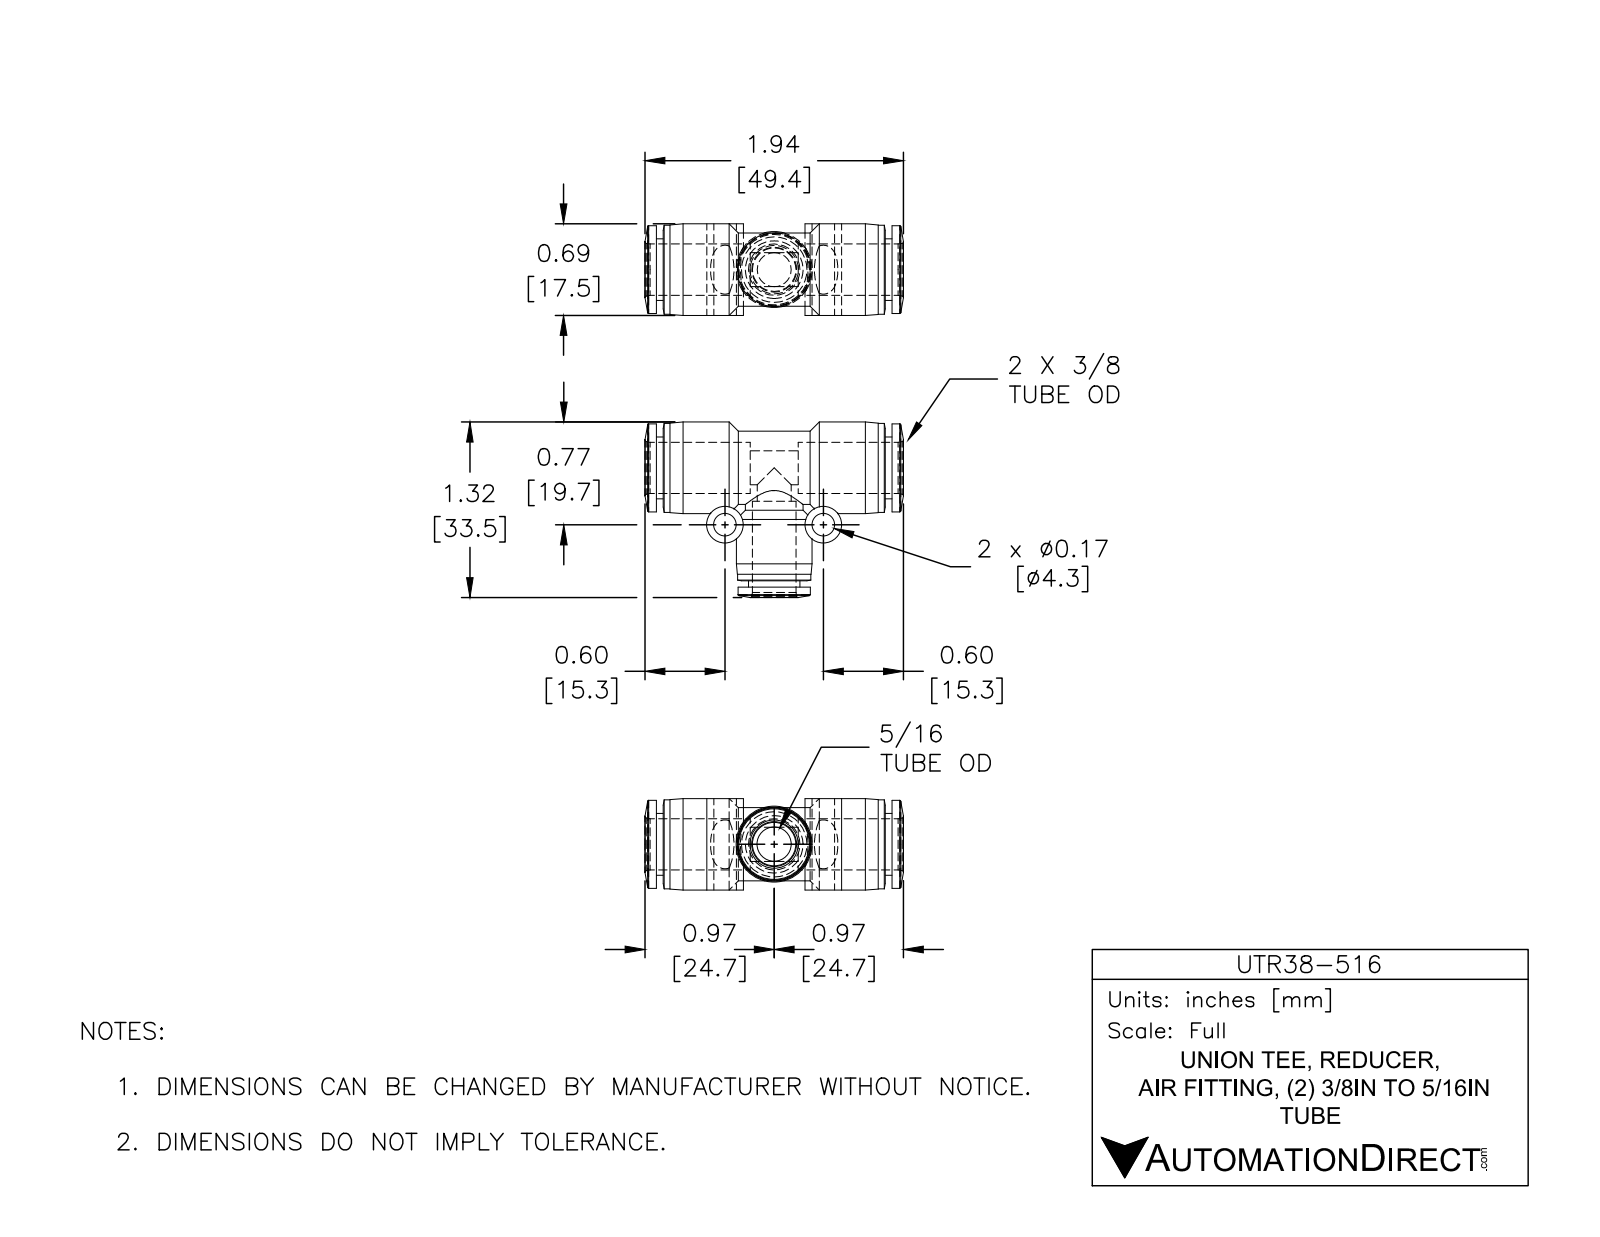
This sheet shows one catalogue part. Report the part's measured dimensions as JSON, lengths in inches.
{"part_name": "UTR38-516", "step_written_by": "SolidWorks 2015 (CONFIG_CONTROL_DESIGN)", "units": "inches", "bodies": {"solids": 1, "faces": 104, "planar": 16, "cylindrical": 46, "other": 42}, "overall_size": [1.945, 1.321, 0.689], "volume_in3": 0.544, "surface_area_in2": 11.28, "round_holes": [[0.169, 2], [0.256, 2], [0.327, 1], [0.386, 1]], "round_bosses_or_shafts": [[0.551, 2], [0.276, 2], [0.689, 1], [0.669, 1], [0.661, 1], [0.571, 1], [0.543, 1], [0.465, 1]], "face_to_face_distances": [0.051, 1.72, 1.772, 0.705, 1.067, 0.654, 1.016, 1.669, 0.689, 0.047], "hole_center_spacings": [0.74]}
